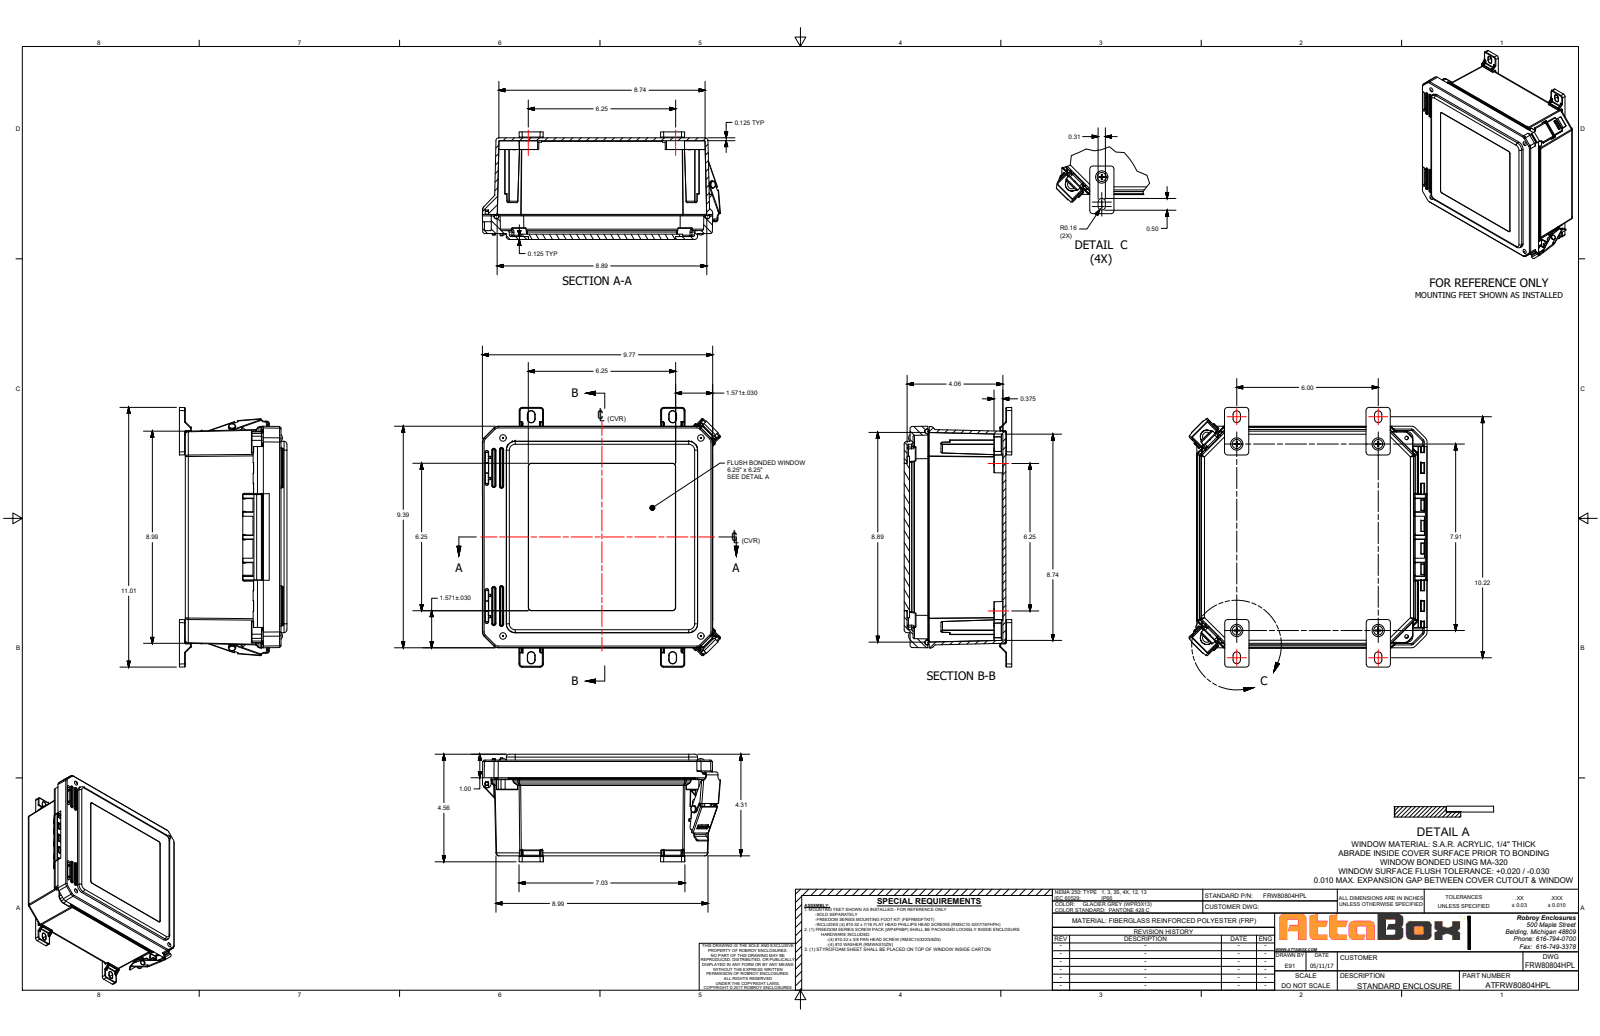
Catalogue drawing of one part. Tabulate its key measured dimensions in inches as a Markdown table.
| quantity | value |
| --- | --- |
| part name | FRW80804HPL |
| STEP written by | SolidWorks 2021 (AUTOMOTIVE_DESIGN) |
| units | inches |
| bodies | 30 solids, 2354 faces (758 planar, 1002 cylindrical, 594 other) |
| overall size | 10.091 × 10.045 × 4.597 |
| volume | 56.67 in³ |
| surface area | 760.5 in² |
| round holes (diameter × count) | 0.152 × 8, 0.159 × 8, 0.135 × 6, 0.135 × 5, 0.137 × 4, 0.15 × 4, 0.156 × 4, 0.252 × 4, 0.253 × 4, 0.219 × 2, 0.227 × 2, 0.313 × 2 |
| round bosses / shafts (diameter × count) | 0.27 × 8, 0.87 × 4, 0.3 × 4, 0.262 × 4, 0.209 × 4, 0.135 × 2, 0.135 × 2, 0.435 × 1 |
| partial cylindrical surfaces (radius × count) | 0.01 × 117, 0.005 × 94, 0.02 × 77, 0.03 × 70, 0.06 × 36, 0.063 × 28, 0.125 × 27, 0.09 × 26 |
| main face-to-face distances | 0.125, 4.184, 4.309, 0.125, 4.059, 0.225, 3.959, 4.084, 3.934, 0.1 |
| hole center spacings | 8.392, 7.41, 7.75, 8.392, 8.414, 0.25, 0.837, 6.25 |
